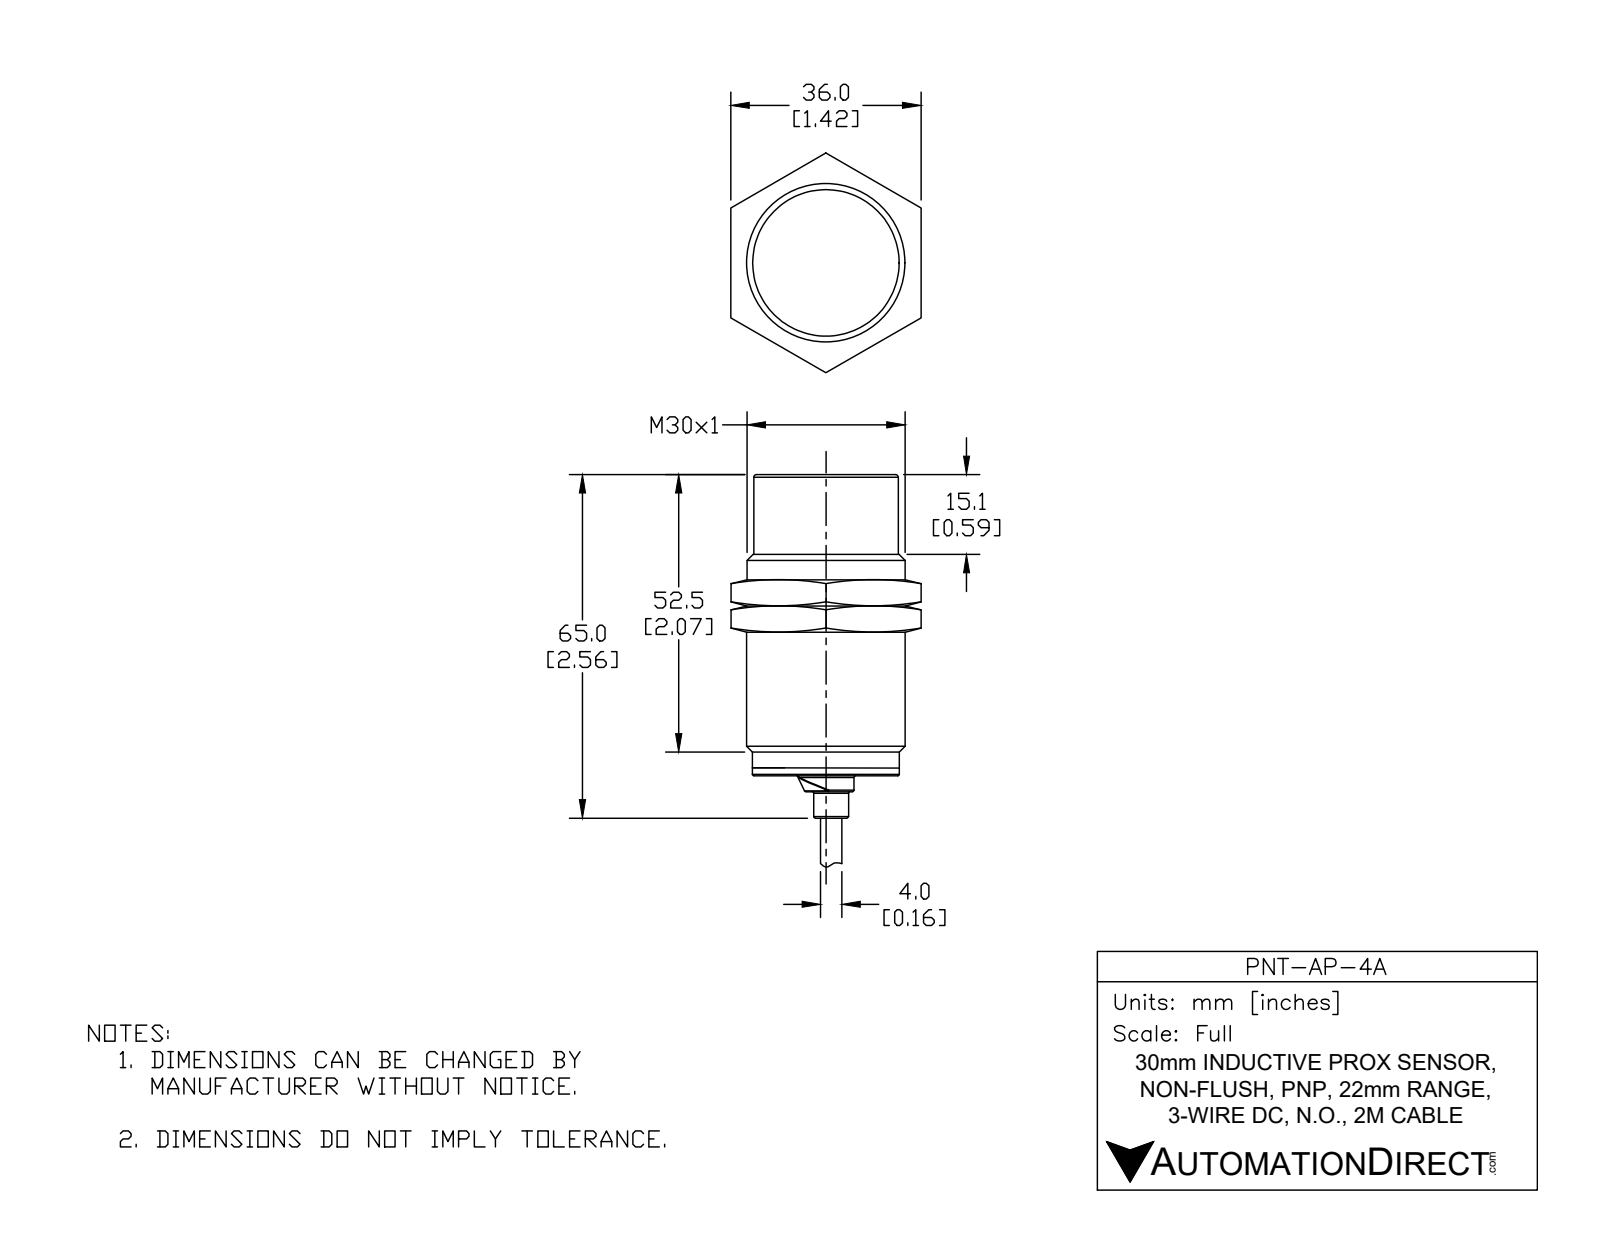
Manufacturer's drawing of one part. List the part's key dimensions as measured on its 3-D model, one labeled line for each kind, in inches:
Part name (STEP PRODUCT): PNT-AP-4A
STEP written by: SolidWorks 2017 (AUTOMOTIVE_DESIGN)
Units: inches
Bodies: 1 solid, 74 faces (14 planar, 30 cylindrical, 30 other)
Overall size (bounding box): 4.559 × 1.181 × 1.181
Volume: 2.487 in³ · Surface area: 11.9 in²
Round holes (diameter × count): ⌀0.162 ×1
Round bosses / shafts (diameter × count): ⌀0.049 ×6, ⌀1.181 ×1, ⌀1.095 ×1, ⌀1.094 ×1, ⌀0.417 ×1, ⌀0.26 ×1, ⌀0.157 ×1
Partial cylindrical surfaces — rounded edges, fillets, slot ends (radius × count): R0.077 ×1
Main face-to-face distances: 2.244, 2.362, 0.118, 2.28, 2.559, 0.315, 0.197, 4.559, 2.315, 2.197
